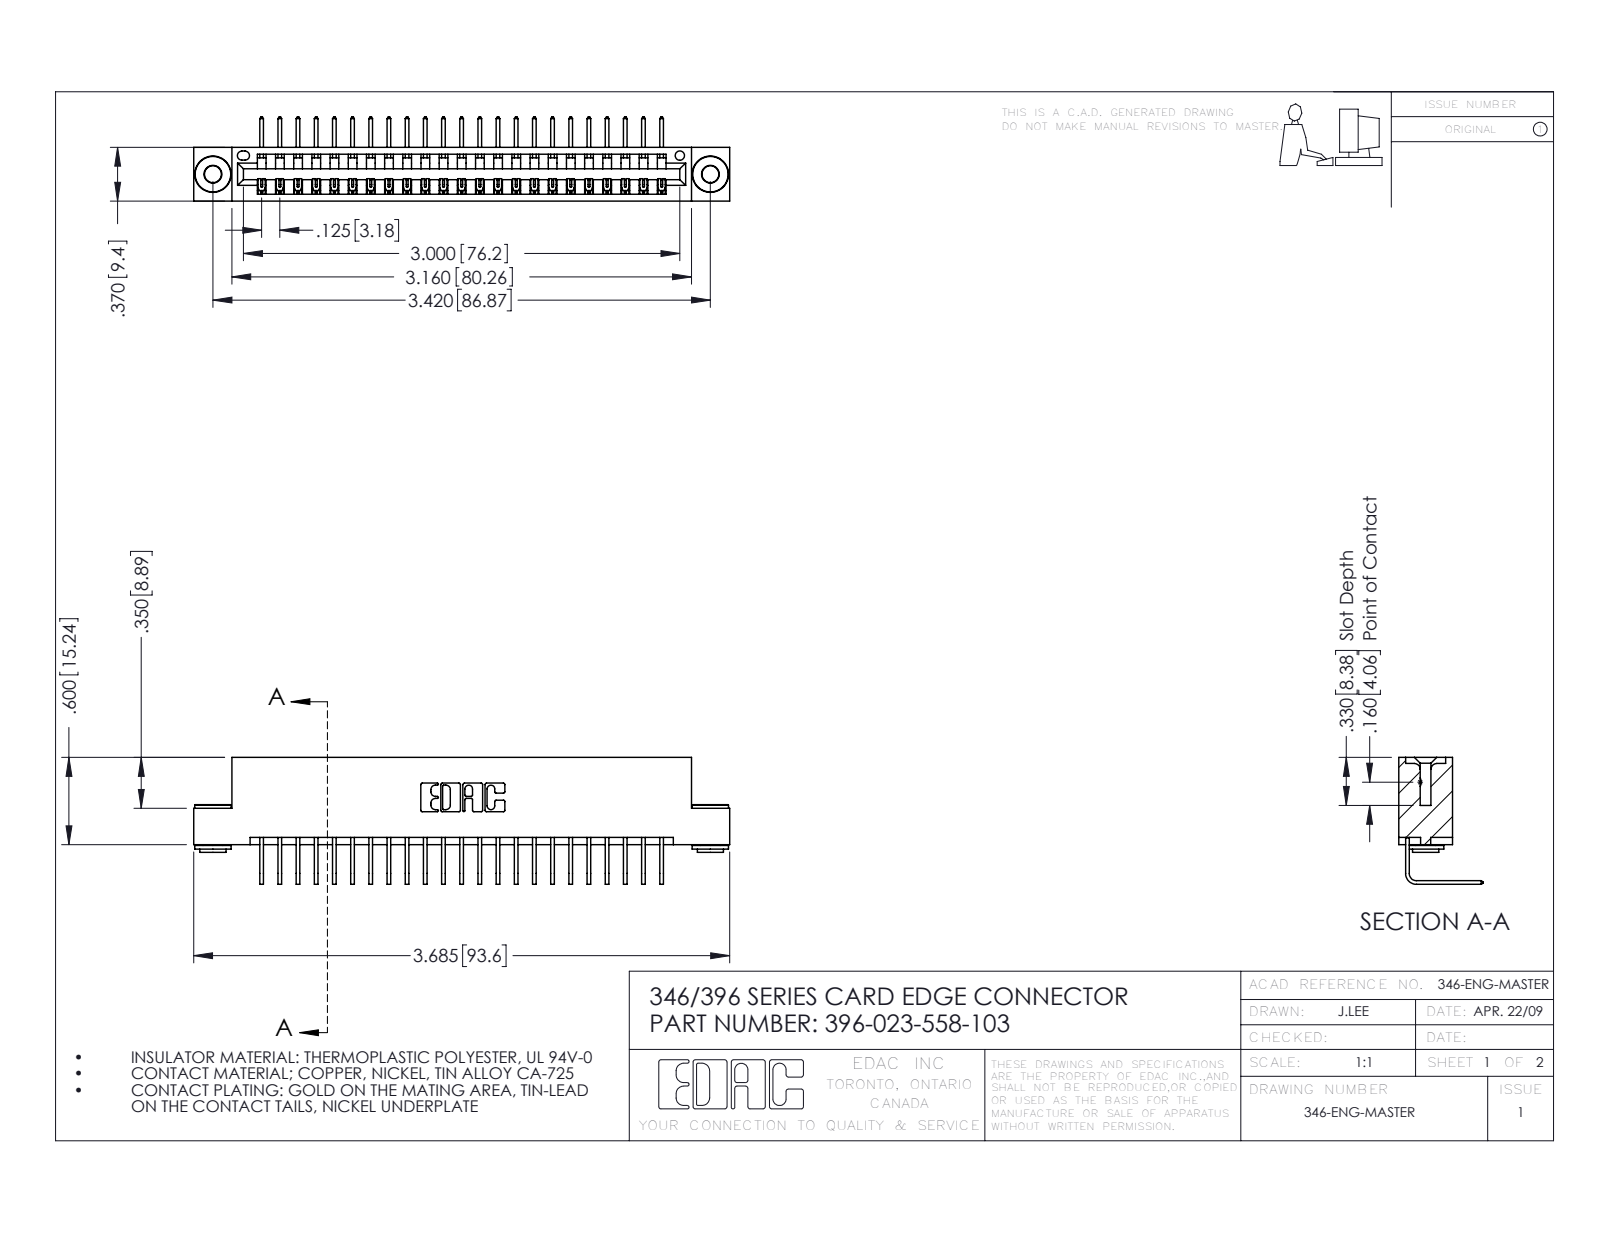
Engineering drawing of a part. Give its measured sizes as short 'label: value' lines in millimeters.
name: 346 Part_Flush Mounting Lugs - 0.156 Dia-TH; 396-023-558-103; 345-292-001_558 Tail - 2; 345-250-002_345-250-002-102
written by: SolidWorks 2016 (CONFIG_CONTROL_DESIGN)
unit: mm
bodies: 26 solids, 1540 faces (1052 planar, 480 cylindrical, 8 other)
size: 93.6 × 22.2 × 14.7
volume: 8 930 mm³; area: 11 630 mm²
holes: 2× ⌀2.9, 2× ⌀4, 1× ⌀1.6
bosses: 2× ⌀6.4, 2× ⌀4.6, 2× ⌀3.5
rounds: 46× R0.2, 22× R0.3, 6× R0.2, 6× R0.8, 3× R0.7, 2× R0.8, 2× R1, 1× R0.4
face distances: 8.2, 1.2, 6.4, 9.4, 0.6, 7.6, 1.8, 3.8, 5.6, 2.5
hole spacings: 6.2, 81.6, 86.9
